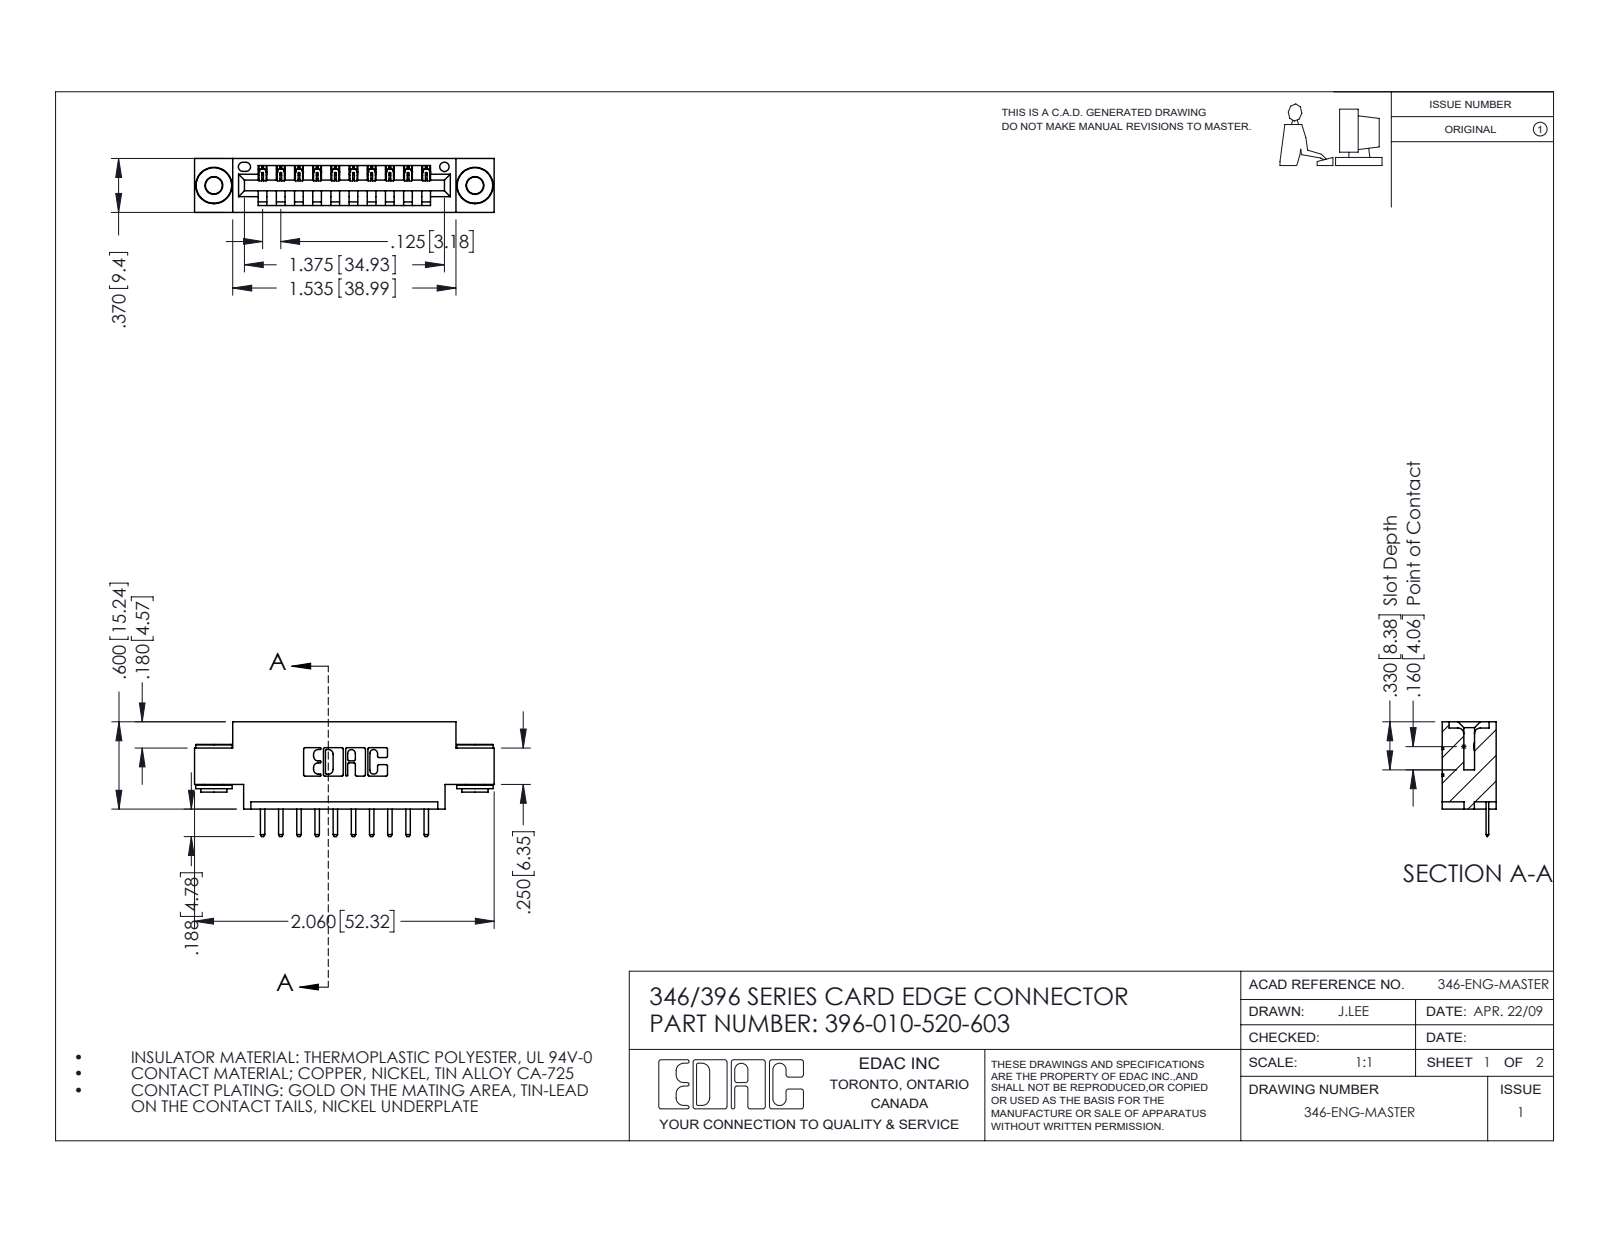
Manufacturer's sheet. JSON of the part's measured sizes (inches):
{"part_name": "345-292-001_345-293-120; 346 Part_0.170 Offset - 0.156 Dia-TH; 396-010-520-603; 345-250-002_345-250-002-102", "step_written_by": "SolidWorks 2016 (CONFIG_CONTROL_DESIGN)", "units": "inches", "bodies": {"solids": 13, "faces": 784, "planar": 510, "cylindrical": 266, "other": 8}, "overall_size": [2.06, 0.788, 0.37], "volume_in3": 0.282, "surface_area_in2": 8.862, "round_holes": [[0.116, 2], [0.156, 2], [0.064, 1]], "round_bosses_or_shafts": [[0.25, 2], [0.18, 2], [0.136, 2]], "partial_cylinders_radius": [[0.01, 22], [0.01, 22], [0.006, 20], [0.007, 6], [0.031, 6], [0.026, 3], [0.031, 2], [0.04, 2]], "face_to_face_distances": [0.25, 0.37, 0.048, 0.322, 0.025, 0.148, 0.222, 0.1, 0.174, 0.275], "hole_center_spacings": [0.246, 1.59, 1.795]}
